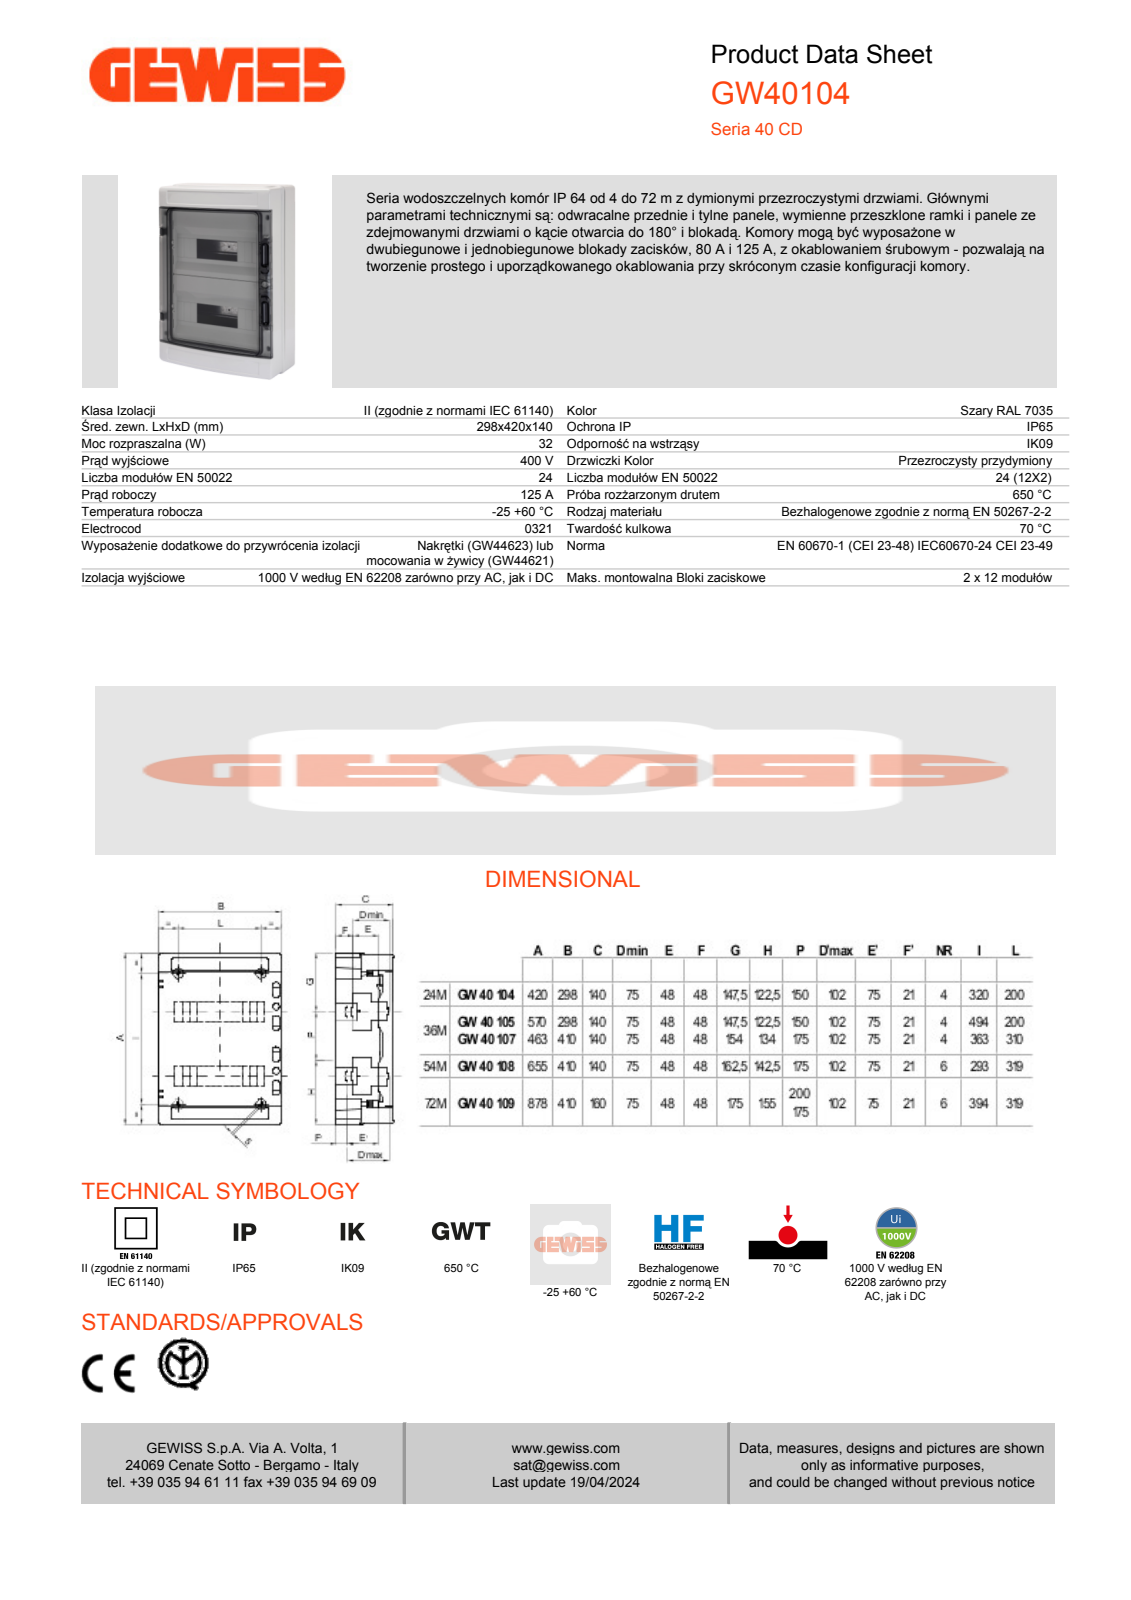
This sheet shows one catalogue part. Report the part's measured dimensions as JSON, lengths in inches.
{"part_name": "GW40104_COMPONENTE_A_AXIRO; GW40104_COMPONENTE_B_AXIRO; GW40104_COMPONENTE_PLASTICA_DX; GW40104_COMPONENTE_PLASTICA_SX (+2 more)", "step_written_by": "CREO PARAMETRIC BY PTC INC, 2020354 (CONFIG_CONTROL_DESIGN)", "units": "inches", "bodies": {"solids": 6, "faces": 1138, "planar": 676, "cylindrical": 244, "other": 218}, "overall_size": [16.496, 11.772, 5.684], "volume_in3": 285.7, "surface_area_in2": 1688, "round_holes": [[0.126, 8], [0.165, 8], [0.335, 4], [0.433, 4], [0.827, 4], [1.433, 1]], "round_bosses_or_shafts": [[0.984, 4], [1.591, 1]], "partial_cylinders_radius": [[0.031, 8], [0.043, 8], [0.071, 8], [0.118, 8], [0.157, 6], [0.374, 6], [0.098, 4], [0.217, 4]], "face_to_face_distances": [0.118, 0.157, 0.039, 0.079, 0.236, 11.535, 3.984, 3.866, 11.654, 16.339], "hole_center_spacings": [0.346, 4.502, 5.906, 8.983, 8.976, 10.745, 0.693, 0.933]}
